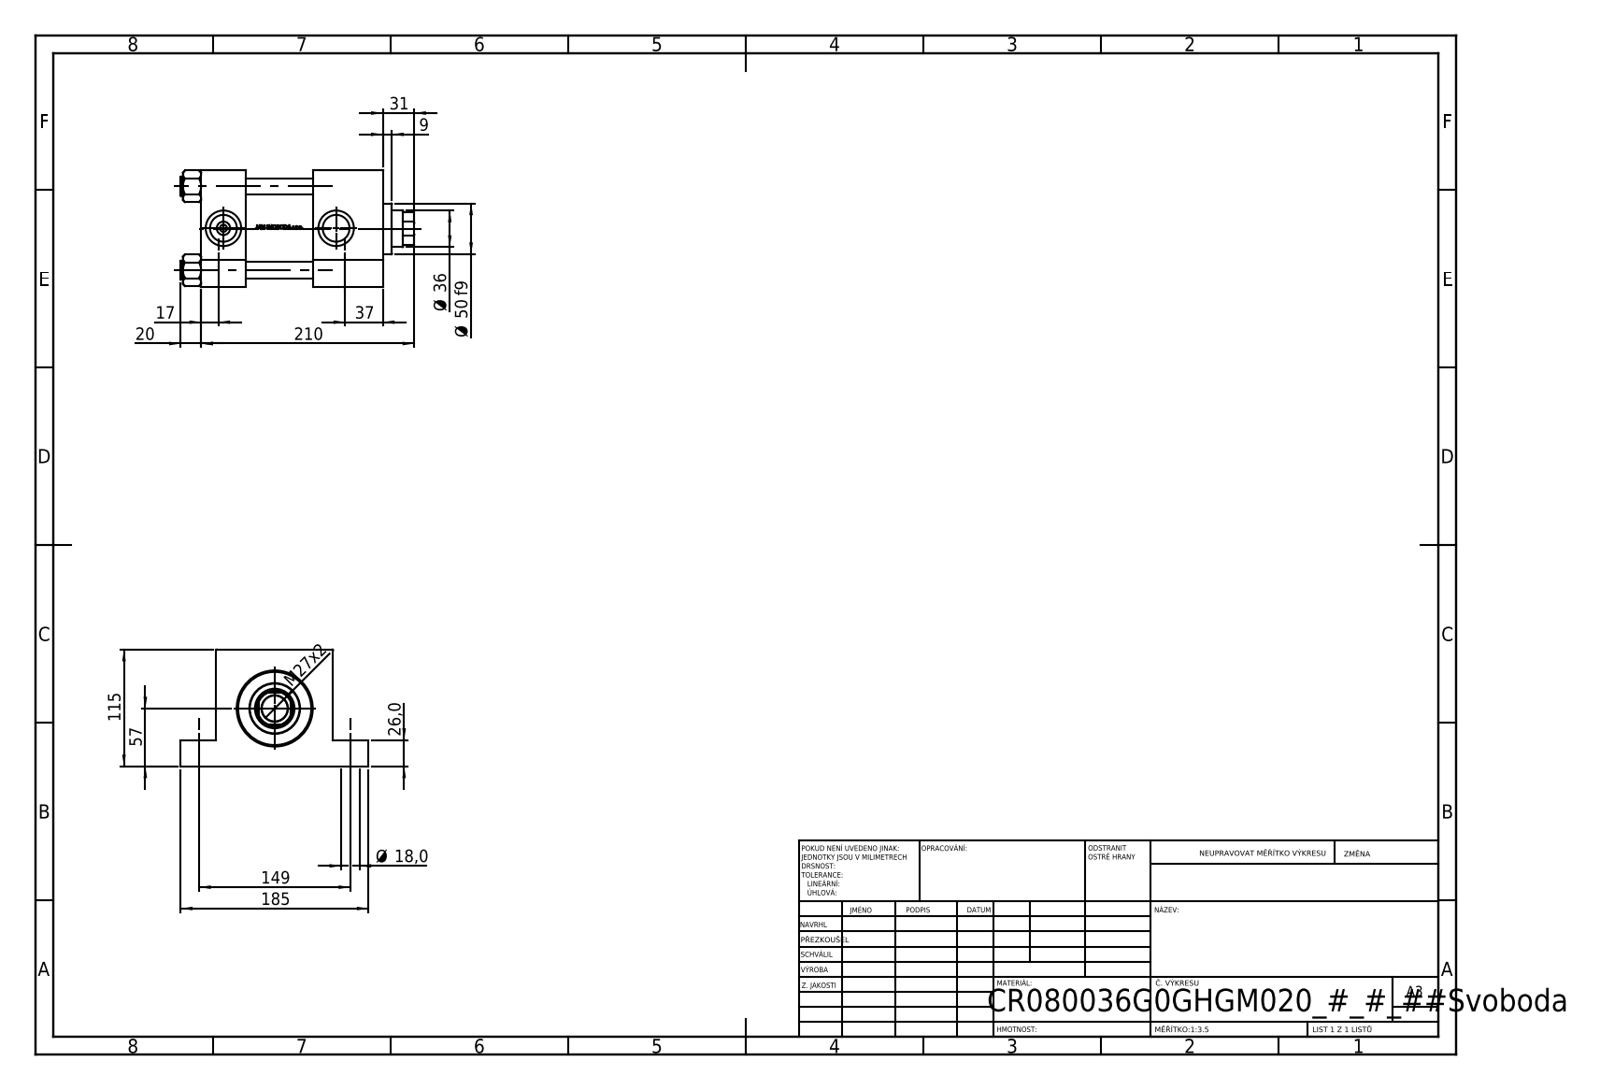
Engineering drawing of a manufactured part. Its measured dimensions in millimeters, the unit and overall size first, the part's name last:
Units: millimetres
Overall size (bounding box): 230 × 185 × 115
Round holes (diameter × count): ⌀16 ×4, ⌀18 ×4, ⌀7 ×2, ⌀26.44 ×2, ⌀35 ×2, ⌀25.5 ×1, ⌀36 ×1, ⌀39 ×1, ⌀61 ×1, ⌀72 ×1, ⌀80 ×1
Round bosses / shafts (diameter × count): ⌀19 ×4, ⌀86 ×1, ⌀50 ×1
Partial cylindrical surfaces — rounded edges, fillets, slot ends (radius × count): R17.5 ×1
Main face-to-face distances: 115, 44, 179, 135, 110, 89, 66, 69, 26, 35
Hole centre spacings: 82.7, 58.13, 58.83, 116.96, 125, 149, 194.49, 111
Volume: 1 990 000 mm³ · Surface area: 289 348 mm²
Bodies: 11 solids, 1135 faces (479 planar, 124 cylindrical, 532 other)
Part name (STEP PRODUCT): NUT_M5_G; V215CR_VCP_G; V215CR_G_TYCINKA; V215_VC_A (+1 more)
STEP written by: SolidWorks 2019 (CONFIG_CONTROL_DESIGN)
